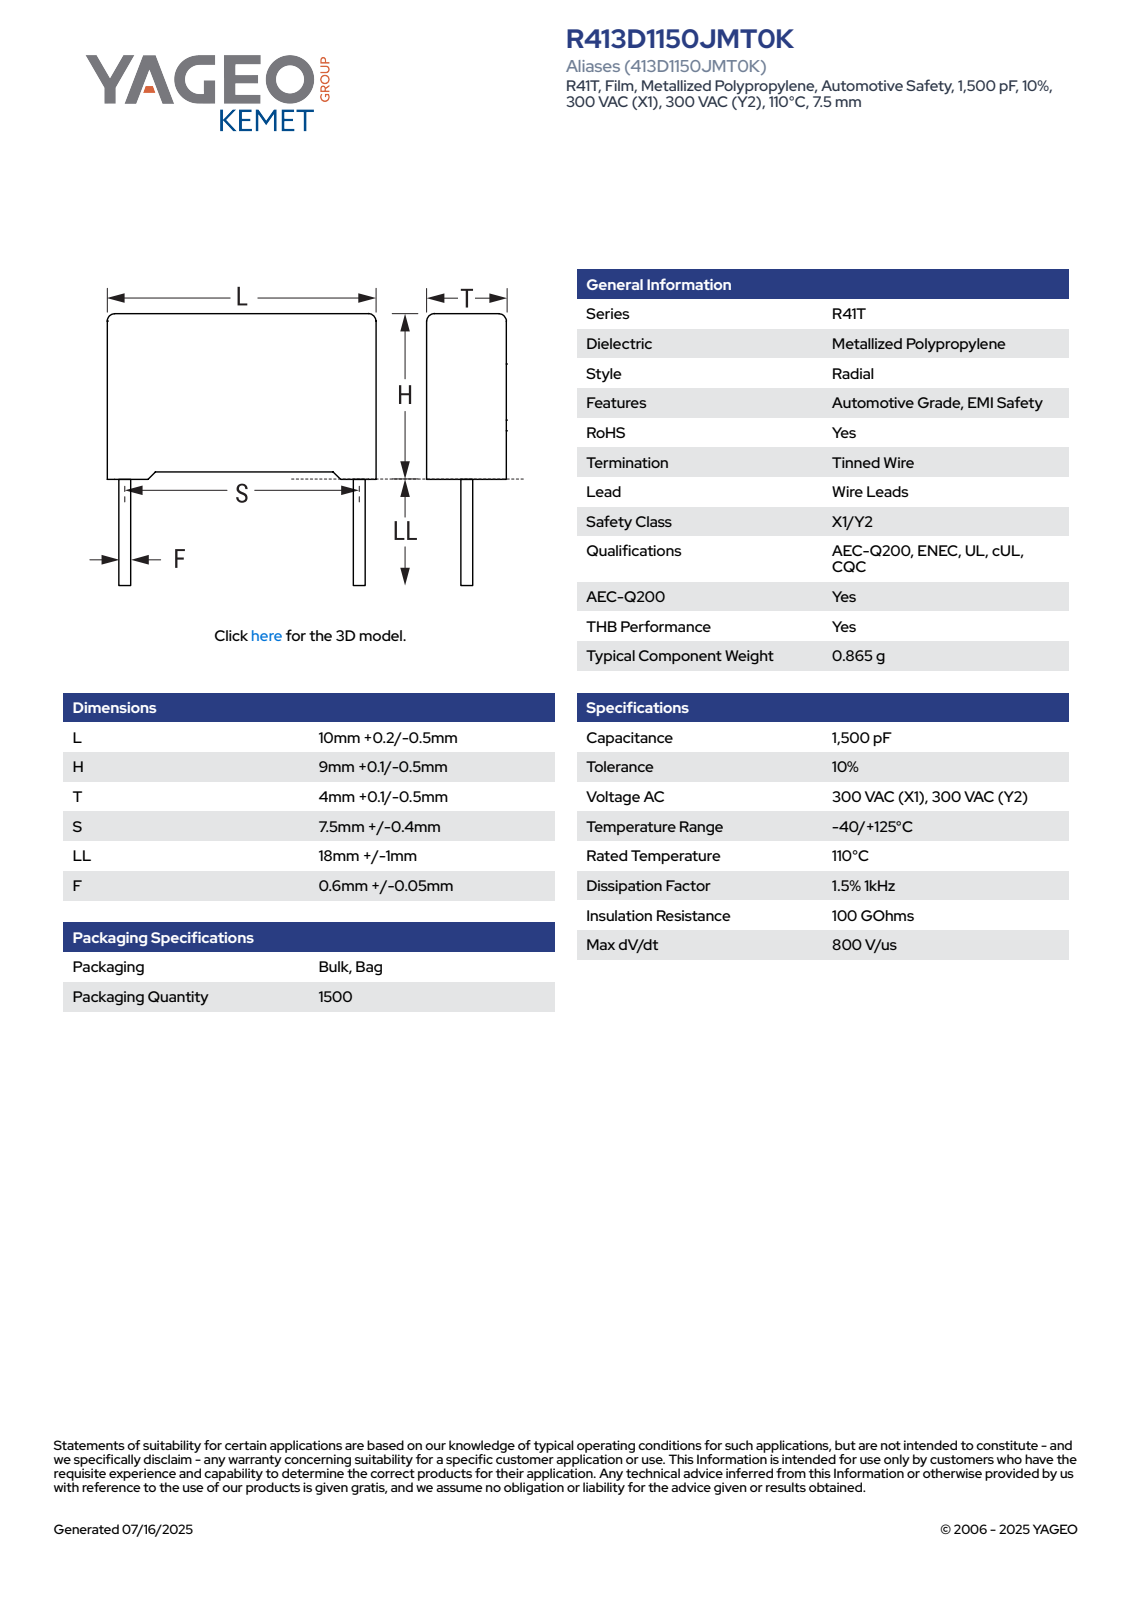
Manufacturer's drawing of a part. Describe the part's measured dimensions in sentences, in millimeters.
The part is named "CFR_RB2_10X9X4_L10.2H9.1T4.1S7.5LL19F0.65". Its 3-D file was written by "SolidWorks 2021 (AUTOMOTIVE_DESIGN)". It is 4 solids with 85 faces: 77 planar, 8 cylindrical and 0 other. Overall it measures 28.1 by 10.2 by 4.11 millimeters. Its volume is 367 cubic millimeters and its surface area 440 square millimeters. Round bosses or shafts: 2 of diameter 0.65. Partial cylindrical surfaces (rounded edges, fillets, slot ends): 4 of radius 0.5. The main face-to-face distances are 4.1, 10.2, 8.35, 0.34, 3.76, 0.75, 9.1, 3.42, 9.86, 0.31.
